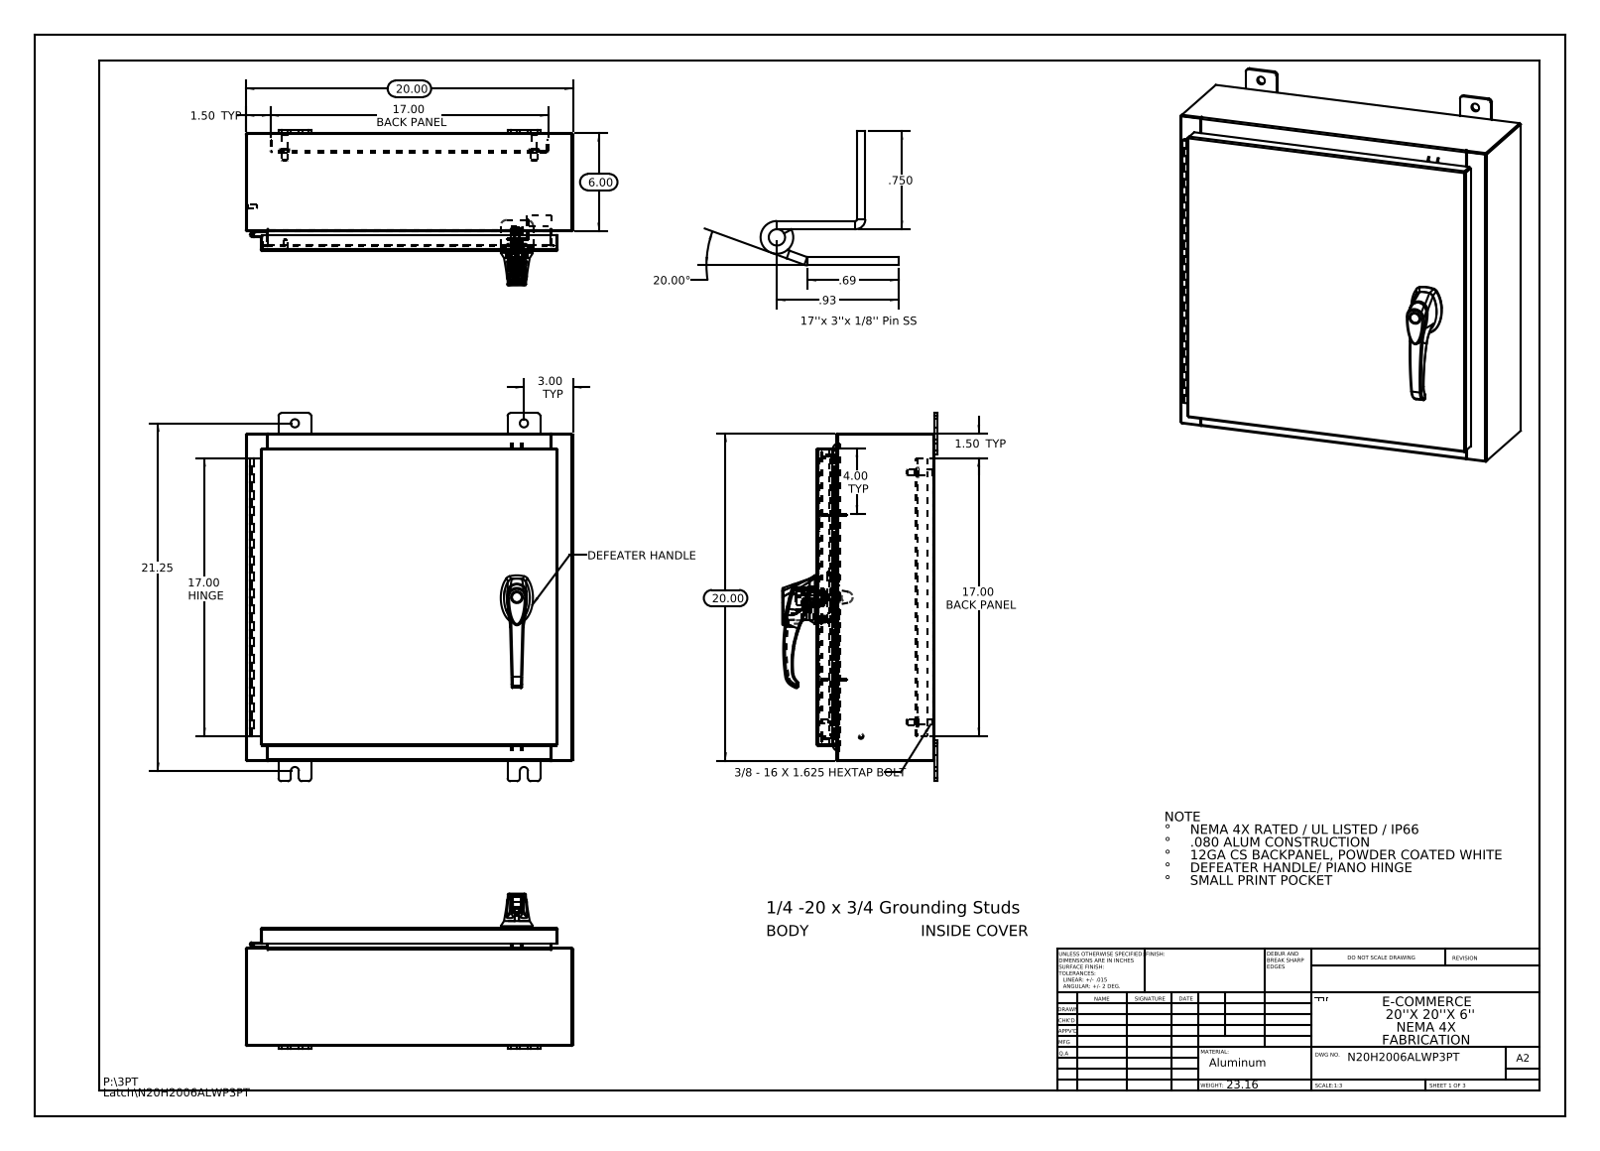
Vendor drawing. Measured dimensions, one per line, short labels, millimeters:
name: Quarter-20 CD Stud; N20H2006ALWP3PT Backpanel; N20H2006ALWP3PT Hinge Enclosure Side2; N20H2006ALWP3PT Defeater Handle Rod (+8 more)
written by: SolidWorks 2013 (CONFIG_CONTROL_DESIGN)
unit: mm
bodies: 37 solids, 2402 faces (835 planar, 869 cylindrical, 698 other)
size: 571.5 × 508 × 241.2
volume: 2 553 000 mm³; area: 2 466 000 mm²
holes: 8× ⌀12.7, 4× ⌀6.4, 3× ⌀3.5, 3× ⌀4.1, 2× ⌀2, 2× ⌀5.2, 2× ⌀8, 2× ⌀11.1, 1× ⌀3.2, 1× ⌀3.2, 1× ⌀5, 1× ⌀7
bosses: 4× ⌀15.9, 4× ⌀9.5, 4× ⌀8.4, 4× ⌀4, 4× ⌀3.6, 3× ⌀8, 3× ⌀6, 1× ⌀30
rounds: 37× R3, 33× R0.2, 24× R4.8, 22× R0.3, 18× R2.2, 15× R1, 12× R0.7, 6× R0.2
face distances: 1.9, 181, 506.1, 179.1, 182.9, 2.6, 25.4, 27.3, 153.7, 155.6
hole spacings: 86.5, 7.5, 15.9, 21.4, 31.8, 33.4, 39.6, 47.2
